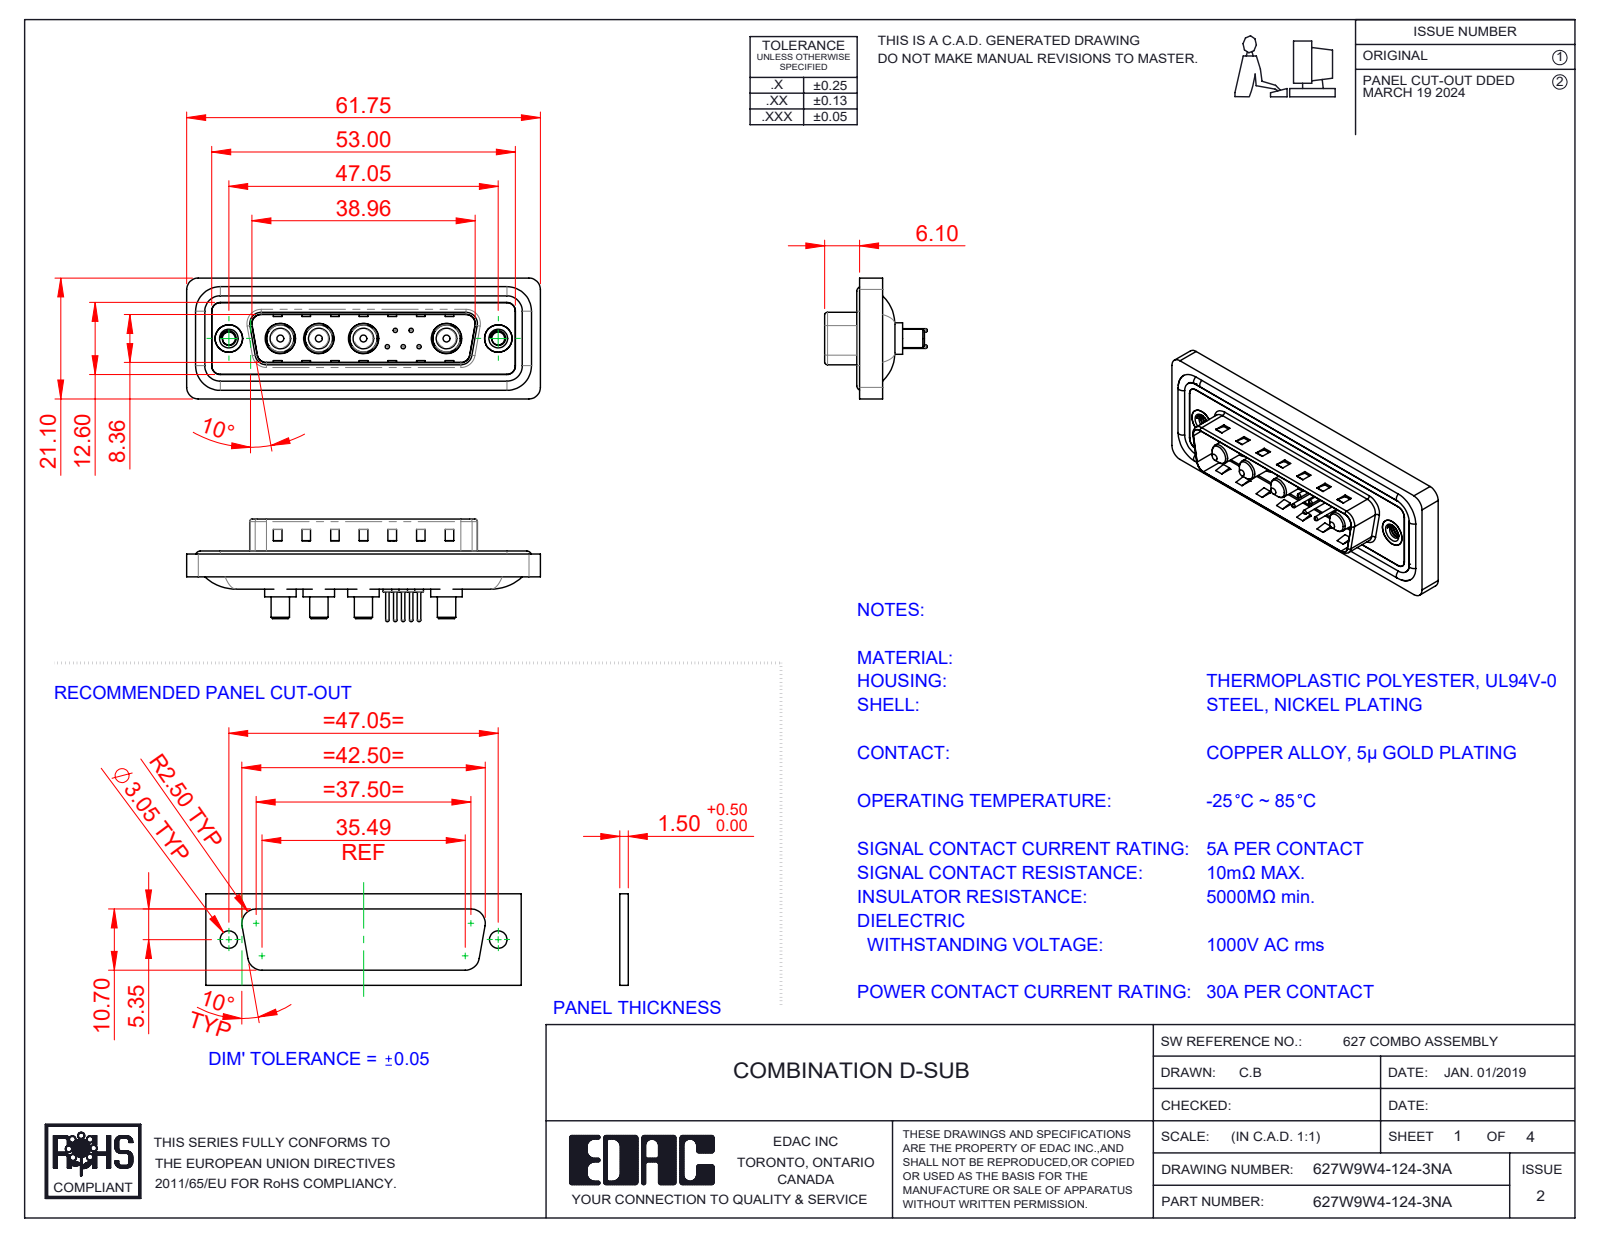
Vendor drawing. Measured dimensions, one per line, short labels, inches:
name: 627Combo Contact Row 2_24; 627Combo Contact Row 1_24; 627W9W4-124-3NA; 627Combo Shell Rear_25 Contacts (+5 more)
written by: SolidWorks 2023 (CONFIG_CONTROL_DESIGN)
unit: in
bodies: 20 solids, 822 faces (284 planar, 336 cylindrical, 202 other)
size: 2.431 × 0.831 × 0.705
volume: 0.454 in³; area: 18.37 in²
holes: 5× ⌀0.03, 5× ⌀0.063, 5× ⌀0.079, 4× ⌀0.191, 4× ⌀0.209, 2× ⌀0.089, 2× ⌀0.157, 2× ⌀0.189, 2× ⌀0.197
bosses: 5× ⌀0.059, 5× ⌀0.024, 4× ⌀0.217, 4× ⌀0.205, 4× ⌀0.187, 4× ⌀0.148, 4× ⌀0.142, 4× ⌀0.126
rounds: 22× R0.059, 18× R0.079, 8× R0.02, 8× R0.063, 4× R0.01, 4× R0.024, 4× R0.026, 4× R0.035
face distances: 0.016, 0.059, 0.043, 0.02, 0.063, 0.122, 0.114, 0.032, 0.377, 0.222
hole spacings: 0.124, 0.109, 0.198, 0.571, 0.109, 0.173, 0.174, 0.197
